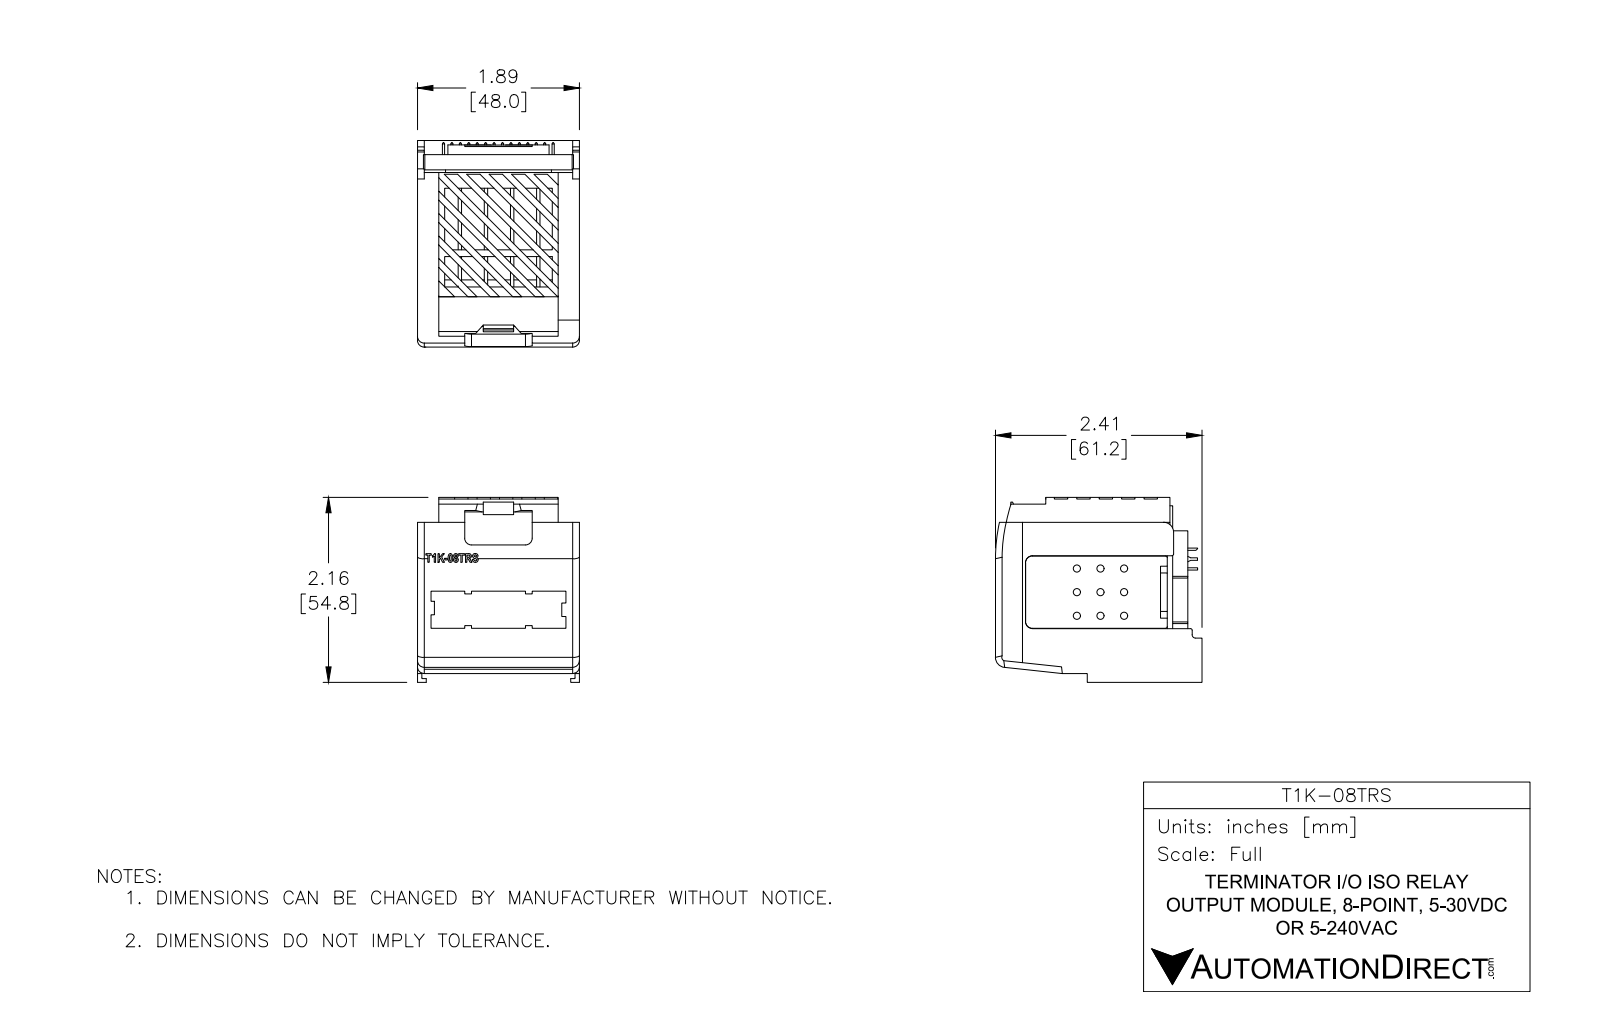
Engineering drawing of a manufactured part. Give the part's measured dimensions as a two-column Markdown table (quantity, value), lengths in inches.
| quantity | value |
| --- | --- |
| part name | T1K-16TRS |
| STEP written by | SolidWorks 2013 (AUTOMOTIVE_DESIGN) |
| units | inches |
| bodies | 1 solid, 651 faces (442 planar, 181 cylindrical, 28 other) |
| overall size | 3.492 × 2.563 × 2.416 |
| volume | 2.774 in³ |
| surface area | 84.51 in² |
| round holes (diameter × count) | 0.118 × 16 |
| round bosses / shafts (diameter × count) | 0.028 × 56 |
| partial cylindrical surfaces (radius × count) | 0.138 × 18, 0.039 × 5, 0.01 × 3, 0.022 × 3, 0.059 × 2, 0.315 × 1, 0.394 × 1, 0.709 × 1 |
| main face-to-face distances | 0.079, 3.413, 2.179, 0.02, 2.354, 3.492, 0.059, 2.176, 2.1, 3.335 |
| hole center spacings | 0.203, 0.406, 0.608, 0.811, 1.014, 1.217, 1.419, 1.622 |
